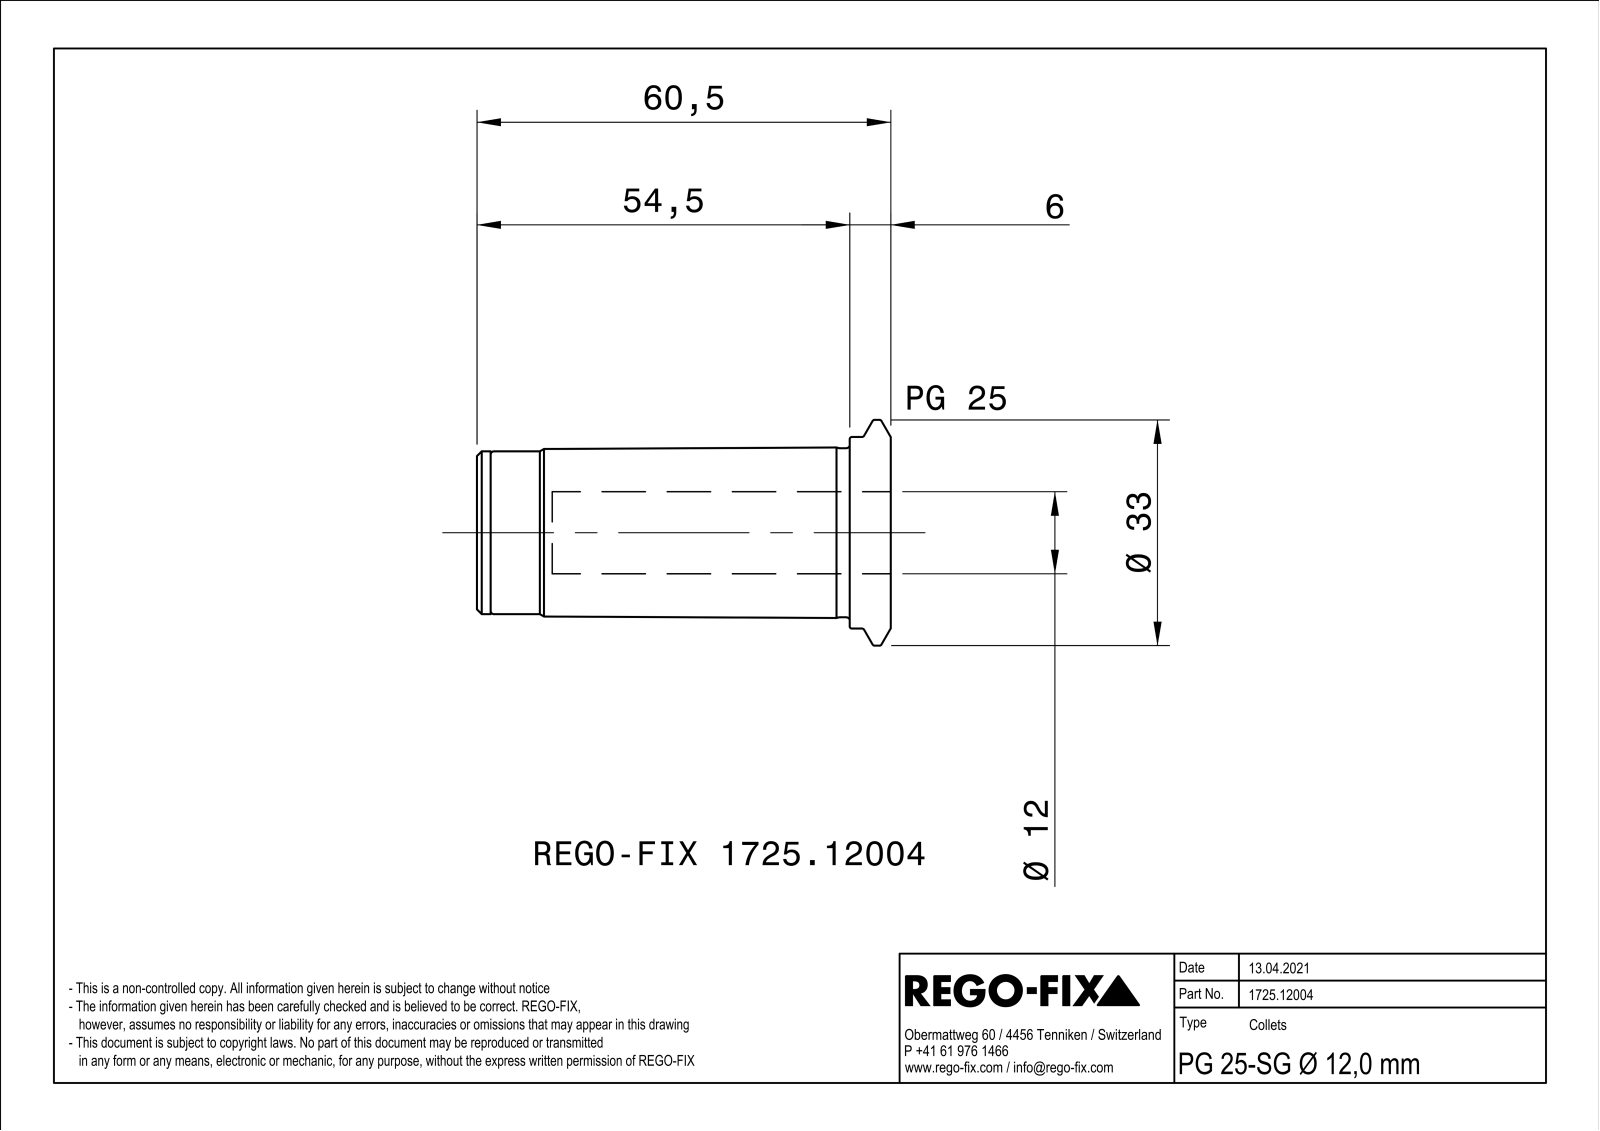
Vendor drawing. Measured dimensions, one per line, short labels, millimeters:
name: NOCUT
written by: SIEMENS PLM Software Solid Edge ST10 (AUTOMOTIVE_DESIGN)
unit: mm
bodies: 1 solid, 85 faces (23 planar, 23 cylindrical, 39 other)
size: 60.5 × 33 × 32.99
holes: 3× ⌀2.5, 1× ⌀5.2, 1× ⌀6.92, 1× ⌀8.2, 1× ⌀12, 1× ⌀20.4, 1× ⌀20.92, 1× ⌀22.2
bosses: 1× ⌀33, 1× ⌀28, 1× ⌀24.7, 1× ⌀23.8
face distances: 1, 60.5, 52.6, 7.9, 58.5, 5.9, 2, 50, 2.6, 8.5
hole spacings: 7.75, 13.43, 13.42
